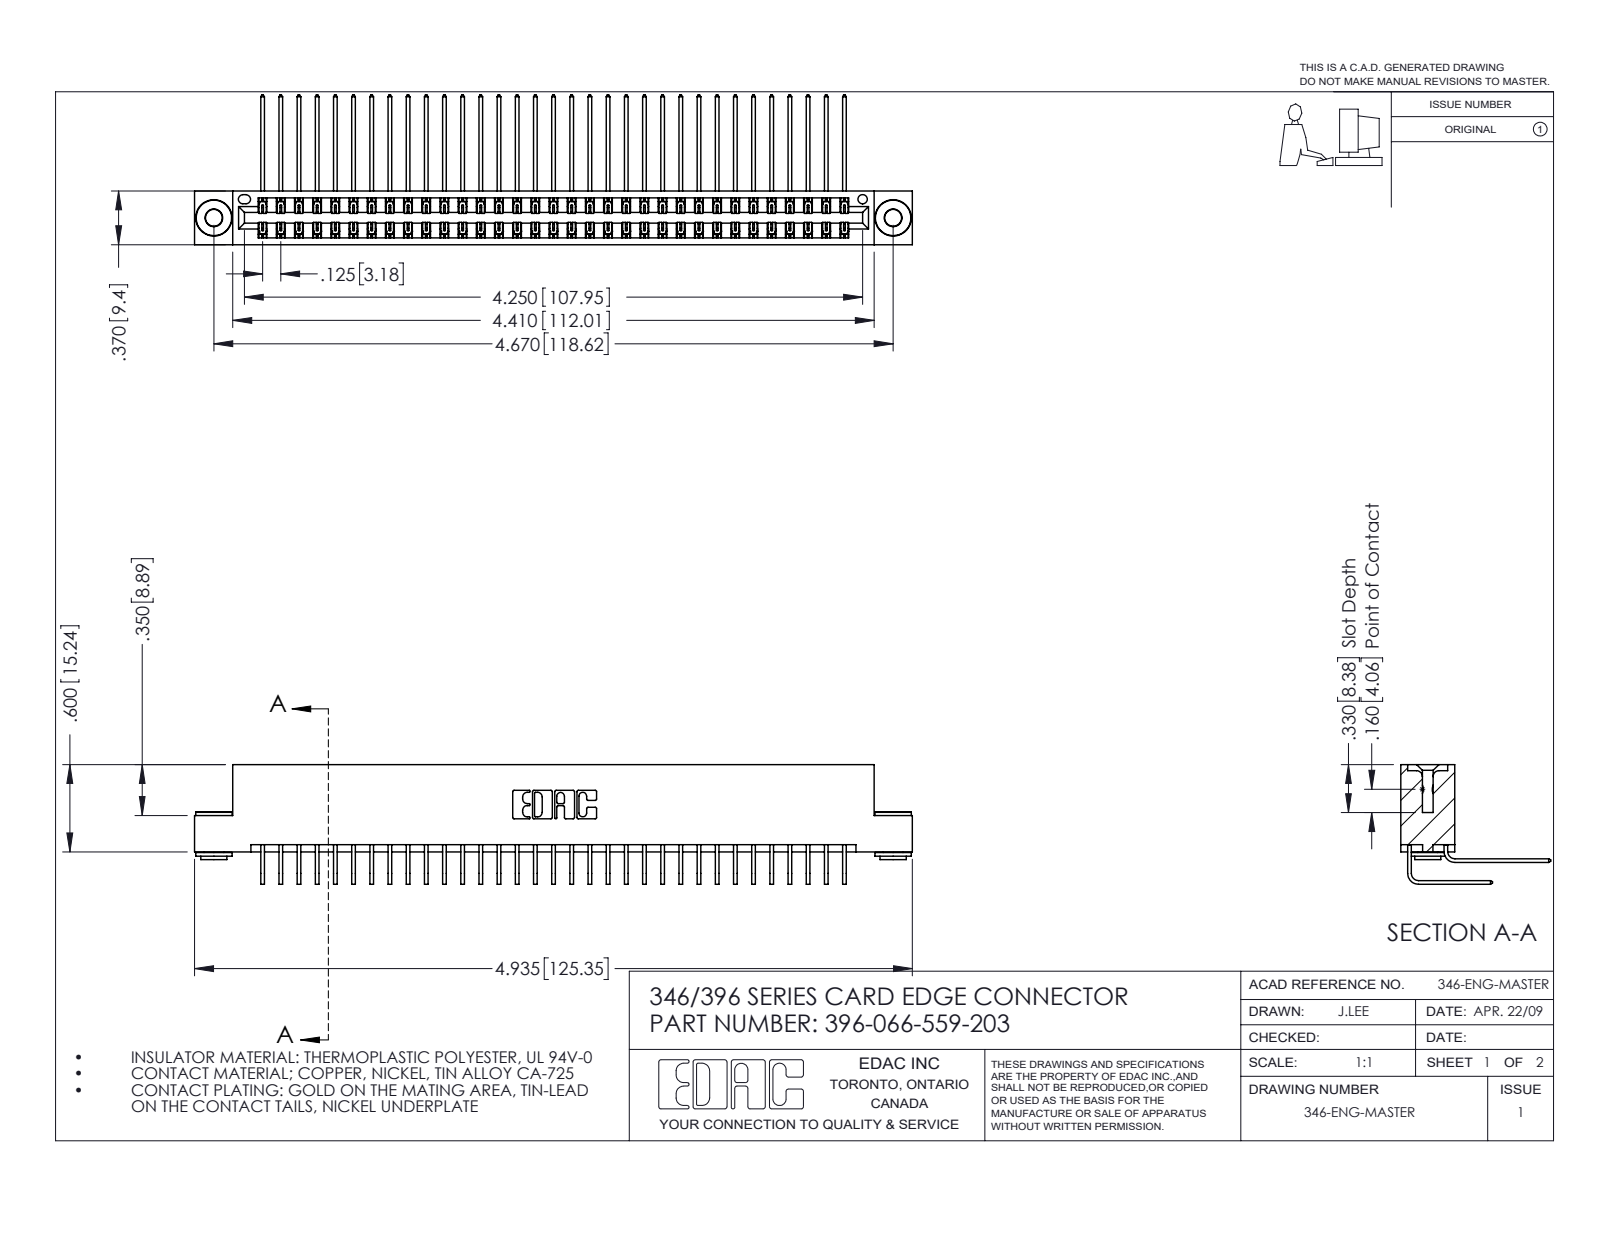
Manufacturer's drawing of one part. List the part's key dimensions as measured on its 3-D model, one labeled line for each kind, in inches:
Part name (STEP PRODUCT): 396-066-559-203; 345-292-001_558 559 Tail - 1; 345-250-002_345-250-002-102; 345-292-001_559 Tail - 2 (+1 more)
STEP written by: SolidWorks 2016 (CONFIG_CONTROL_DESIGN)
Units: inches
Bodies: 69 solids, 3724 faces (2528 planar, 1188 cylindrical, 8 other)
Overall size (bounding box): 4.935 × 1.03 × 0.823
Volume: 0.766 in³ · Surface area: 29.69 in²
Round holes (diameter × count): ⌀0.116 ×2, ⌀0.156 ×2, ⌀0.064 ×1
Round bosses / shafts (diameter × count): ⌀0.25 ×2, ⌀0.18 ×2, ⌀0.136 ×2
Partial cylindrical surfaces — rounded edges, fillets, slot ends (radius × count): R0.006 ×99, R0.01 ×22, R0.007 ×6, R0.031 ×6, R0.026 ×3, R0.014 ×2, R0.022 ×2, R0.024 ×2
Main face-to-face distances: 0.048, 0.322, 0.025, 0.25, 0.37, 0.072, 0.298, 0.275, 0.148, 0.222
Hole centre spacings: 0.246, 4.462, 4.67
